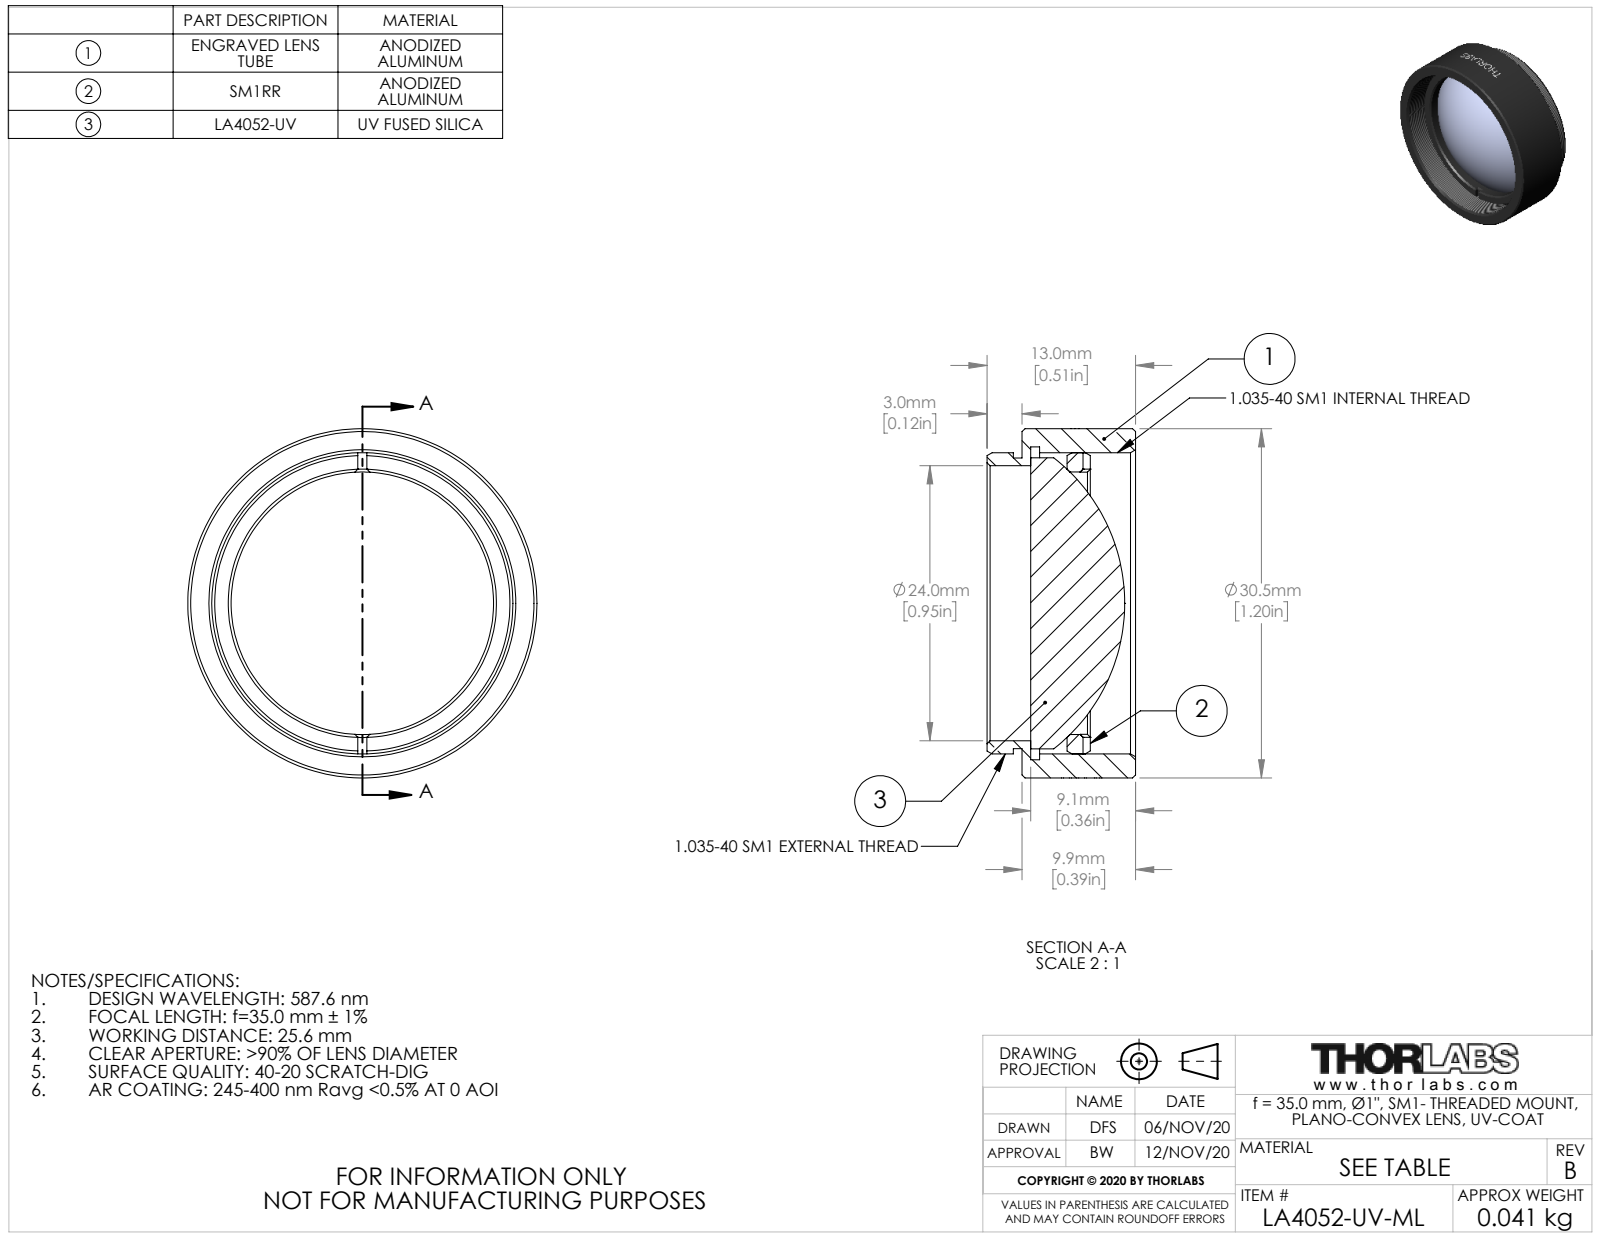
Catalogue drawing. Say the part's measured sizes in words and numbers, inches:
The part is named "24451-E0W". Its 3-D file was written by "SolidWorks 2018 (CONFIG_CONTROL_DESIGN)". It is 3 solids with 114 faces: 20 planar, 70 cylindrical and 24 other. Overall it measures 1.2 by 1.2 by 0.51 inches. Its volume is 0.31 cubic inches and its surface area 7.293 square inches. Round holes: 1 of diameter 0.902, 1 of diameter 0.945, 1 of diameter 1.035, 1 of diameter 1.075. Round bosses or shafts: 1 of diameter 1.2, 1 of diameter 1.035, 1 of diameter 1, 1 of diameter 0.999. The main face-to-face distances are 0.03, 0.39, 0.36, 0.155, 0.124, 0.235, 0.235, 0.205, 0.08, 0.155.
